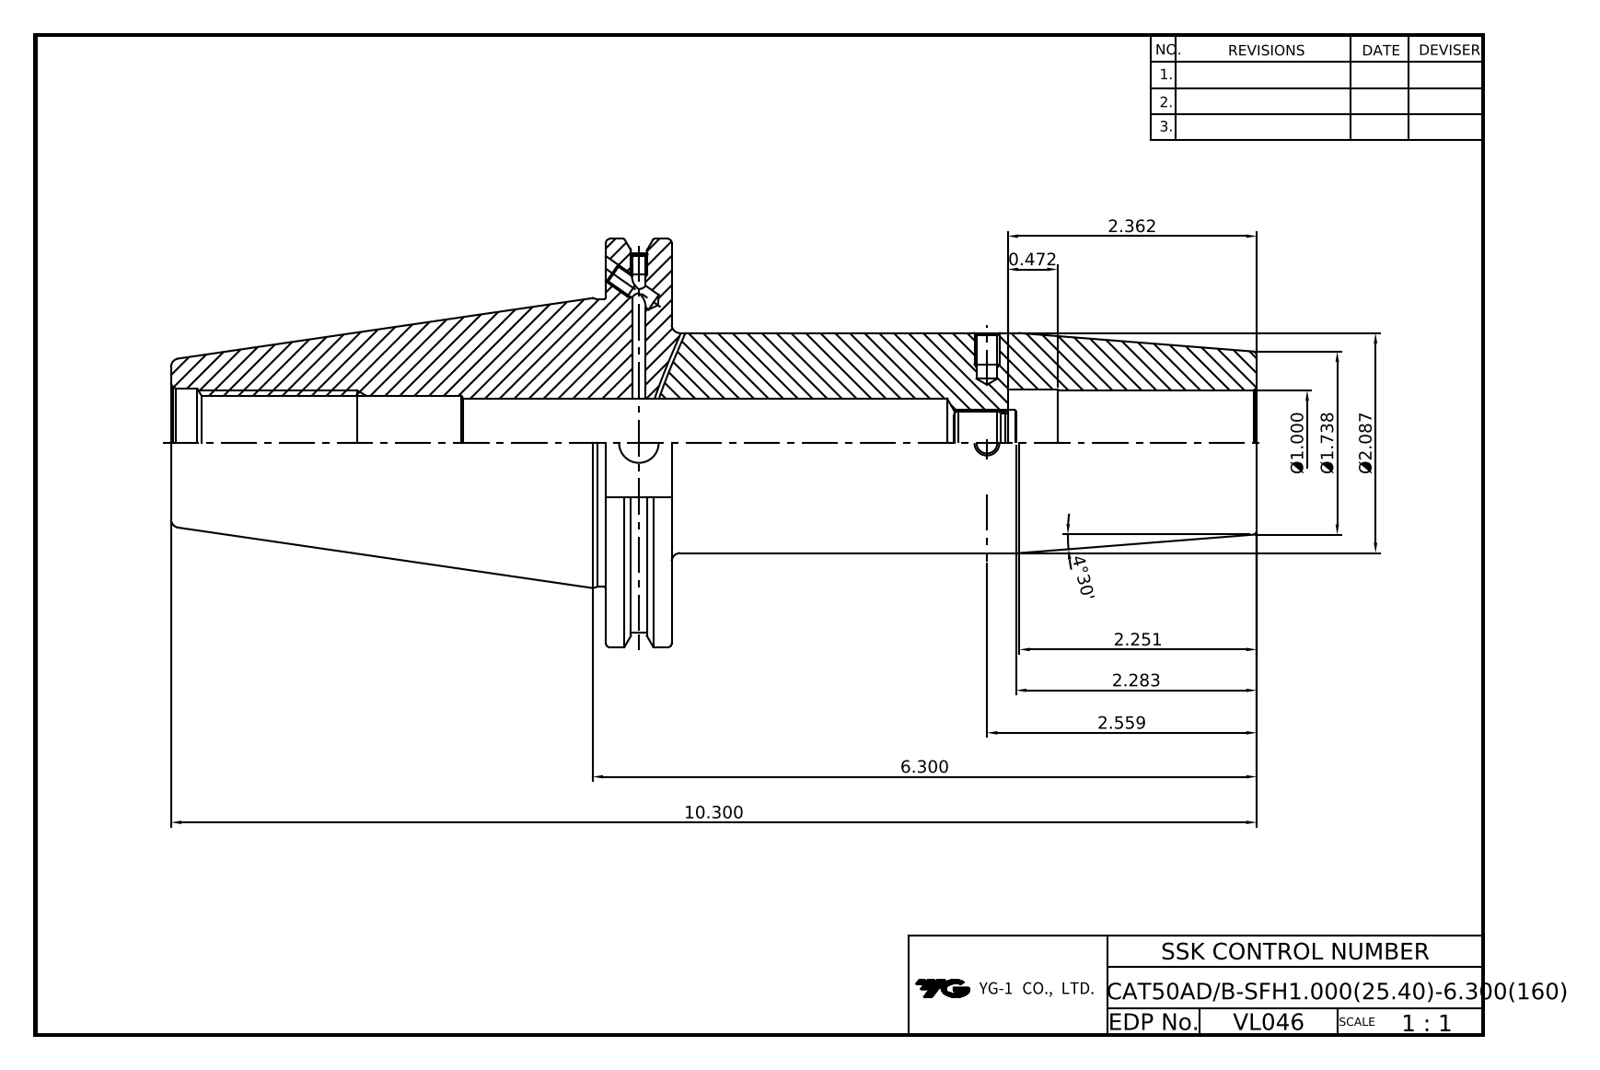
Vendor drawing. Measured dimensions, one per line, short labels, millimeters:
name: LO-CAT50ADB-SFH25.4-160
written by: Autodesk Inventor 2025 (AUTOMOTIVE_DESIGN)
unit: mm
bodies: 1 solid, 84 faces (37 planar, 26 cylindrical, 21 other)
size: 261.6 × 98.42 × 94.69
volume: 555 520 mm³; area: 76 324 mm²
holes: 2× ⌀3.24, 2× ⌀4.13, 2× ⌀4.2, 2× ⌀5, 1× ⌀9.53, 1× ⌀14.92, 1× ⌀21.97, 1× ⌀25.4, 1× ⌀26.2, 1× ⌀26.6
bosses: 1× ⌀98.42, 1× ⌀91.29, 1× ⌀69.25, 1× ⌀53
face distances: 15.88, 156.83, 140.95, 104.77, 120.65, 261.6, 201.6, 96.83, 80.95, 60
